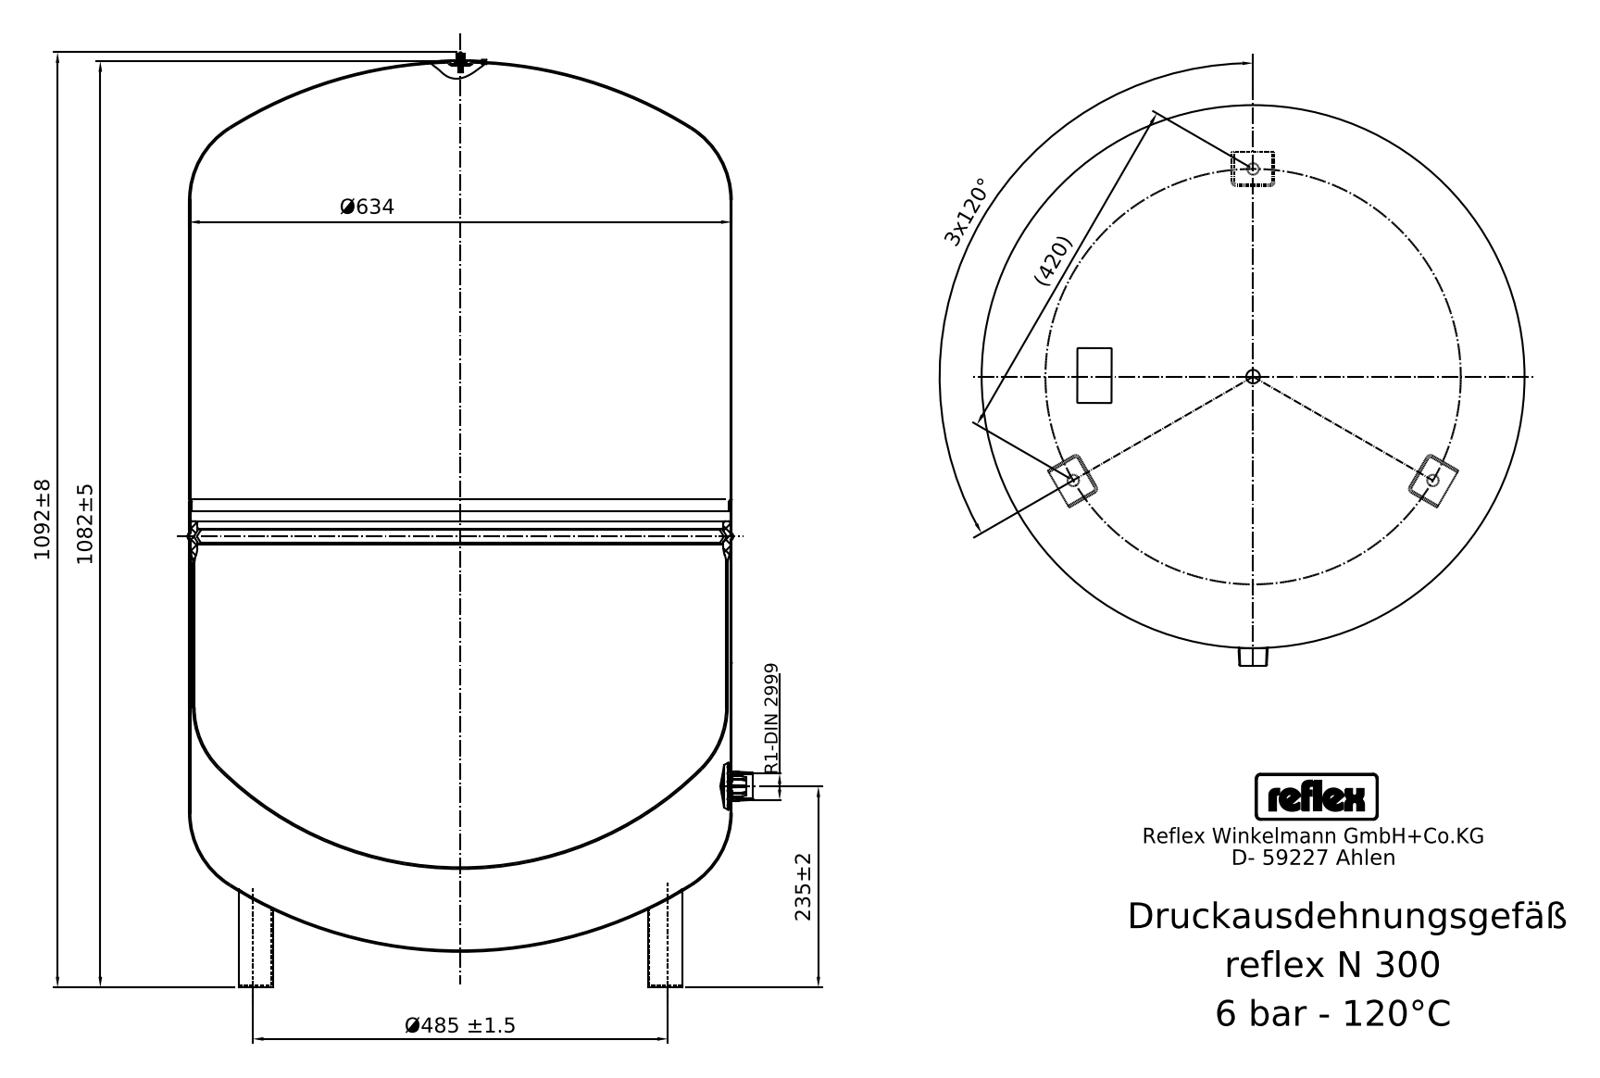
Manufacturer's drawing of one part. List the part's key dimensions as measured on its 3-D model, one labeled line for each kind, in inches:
STEP written by: Mechanical Desktop 2008 (CONFIG_CONTROL_DESIGN)
Units: inches
Bodies: 16 solids, 246 faces (100 planar, 91 cylindrical, 55 other)
Overall size (bounding box): 43.396 × 26.16 × 25.39
Volume: 17 900 in³ · Surface area: 5 738 in²
Round holes (diameter × count): ⌀0.528 ×3, ⌀0.333 ×1, ⌀1.012 ×1
Round bosses / shafts (diameter × count): ⌀24.961 ×1, ⌀24.961 ×1, ⌀1.327 ×1, ⌀0.404 ×1, ⌀0.213 ×1, ⌀0.142 ×1
Partial cylindrical surfaces — rounded edges, fillets, slot ends (radius × count): R0.039 ×15, R0.098 ×15, R0.197 ×15, R0.155 ×4, R0.062 ×3, R0.106 ×2, R0.186 ×2, R0.256 ×2
Main face-to-face distances: 28.189, 0.098, 1.87, 1.772, 1.969, 14.094, 0.079, 8.15, 22.244, 36.339
Hole centre spacings: 9.547, 16.536
